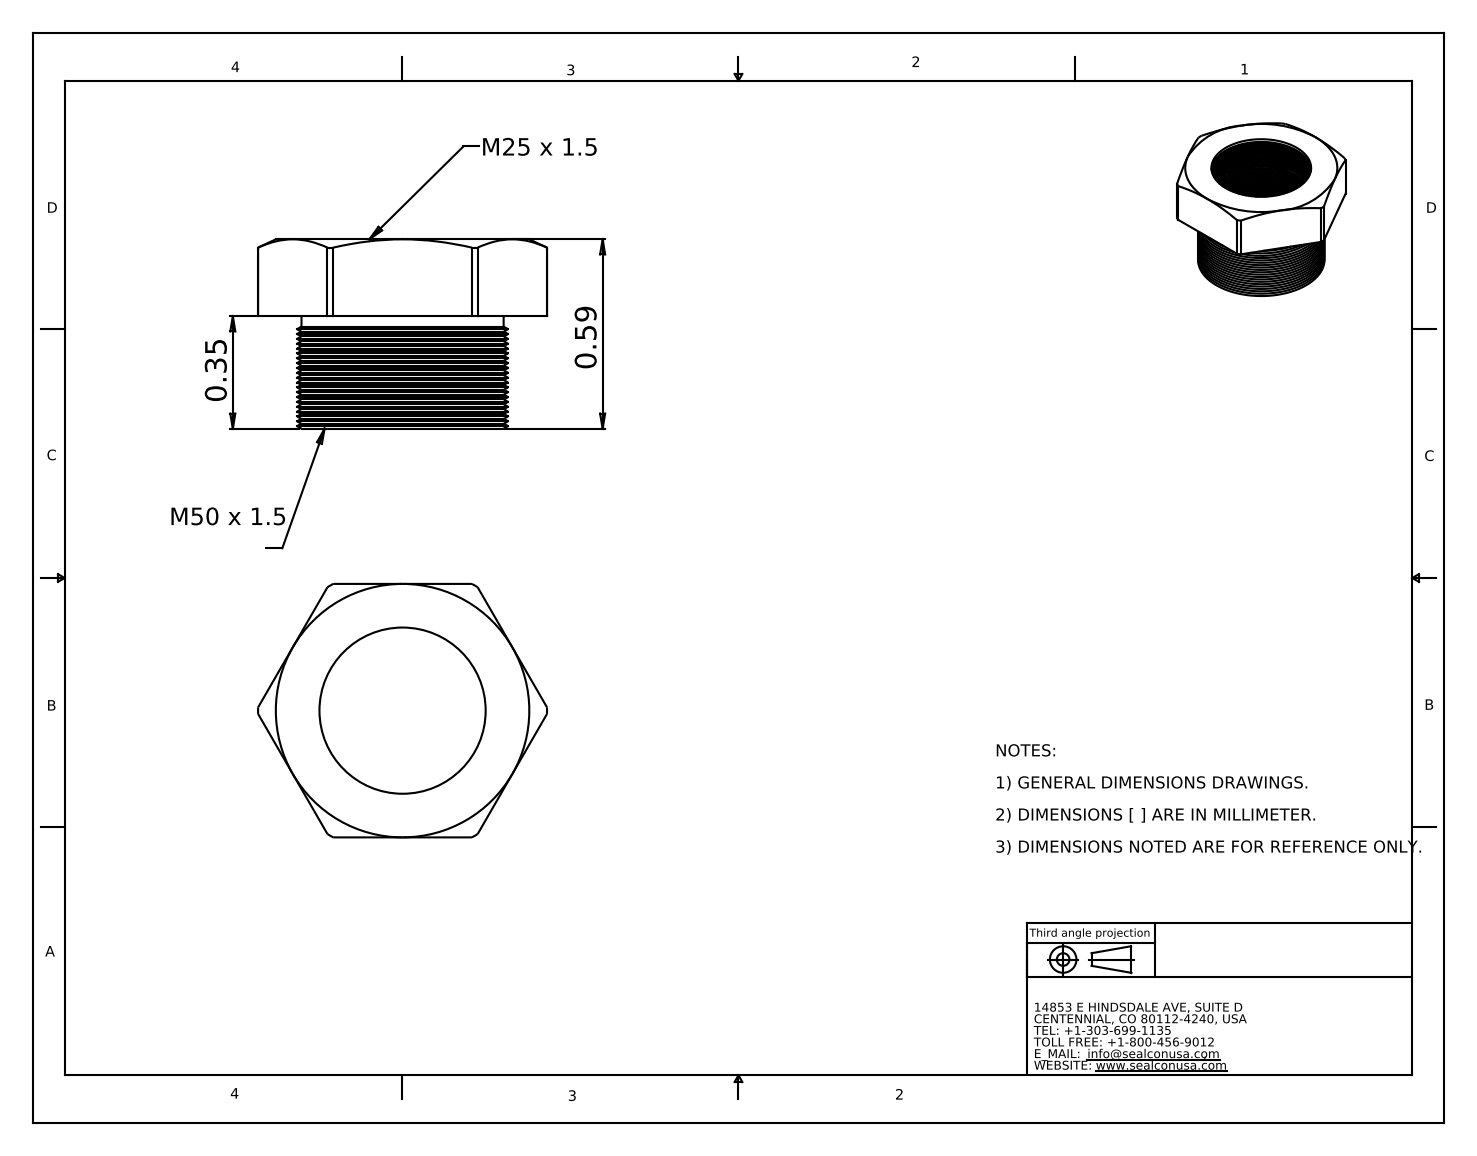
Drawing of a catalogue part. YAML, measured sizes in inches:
part_name: "RM-5025-SS"
step_written_by: "SolidWorks 2008 (CONFIG_CONTROL_DESIGN)"
units: inches
bodies: {solids: 1, faces: 329, planar: 9, cylindrical: 85, other: 235}
overall_size: [0.901, 0.79, 0.59]
volume: 0.116
surface_area: 4.587
round_holes:
  - {diameter: 0.518, count: 1}
  - {diameter: 0.63, count: 1}
partial_cylinders:
  - {radius: 0.45, count: 1}
face_to_face_distances: [0.79, 0.24, 0.35, 0.59]
